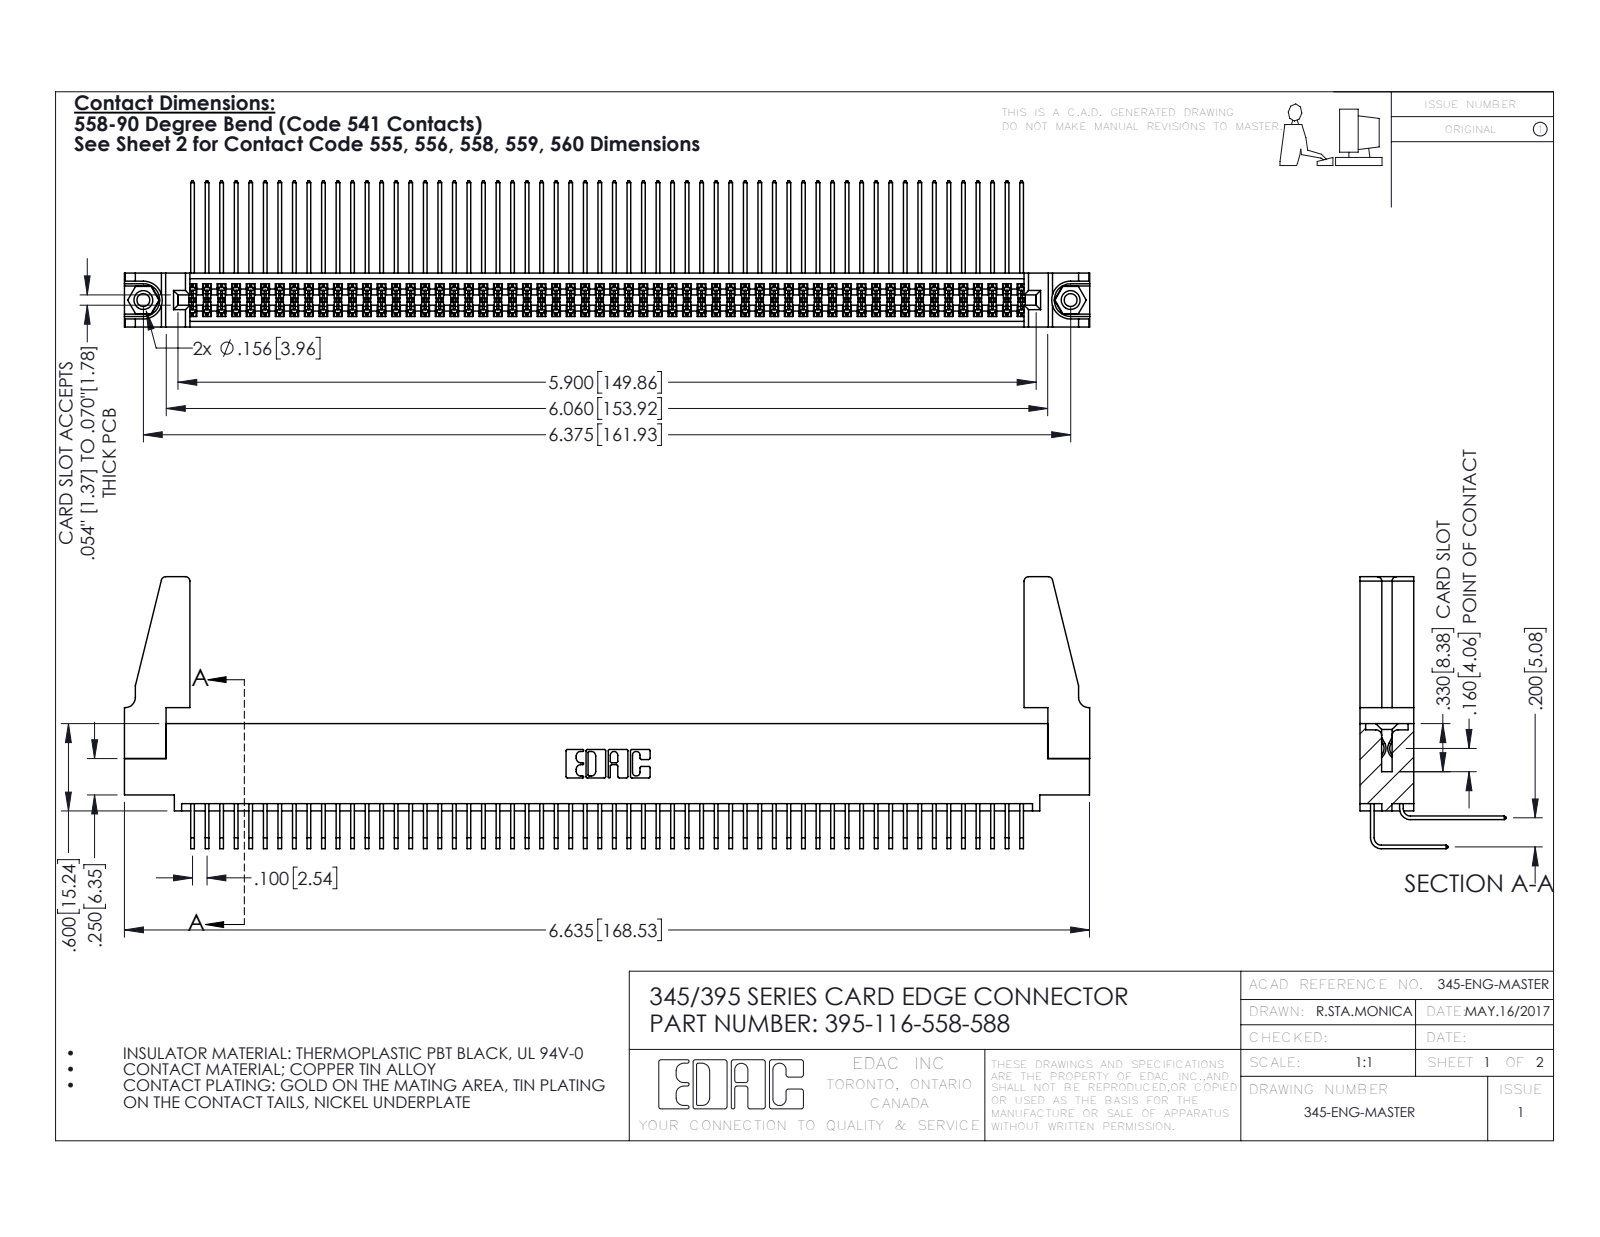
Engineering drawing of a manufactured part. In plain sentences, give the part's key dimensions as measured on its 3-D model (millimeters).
The part is named "395-116-558-588; 345-292-001_558 559 Tail - 1; 345-250-001_345-250-001-102; 345 Part_0.110 Offset - 0.156 Dia-TH (+2 more)". Its 3-D file was written by "SolidWorks 2016 (CONFIG_CONTROL_DESIGN)". It is 121 solids with 6286 faces: 4216 planar, 2054 cylindrical and 16 other. Overall it measures 168.6 by 47.5 by 25.5 millimeters. Its volume is 20 370 cubic millimeters and its surface area 31 970 square millimeters. Round holes: 2 of diameter 2.3, 2 of diameter 3.2, 2 of diameter 4, 1 of diameter 1.6. Round bosses or shafts: 2 of diameter 3.9. Partial cylindrical surfaces (rounded edges, fillets, slot ends): 174 of radius 0.2, 22 of radius 0.3, 8 of radius 0.8, 6 of radius 0.2, 6 of radius 0.8, 3 of radius 0.7, 2 of radius 0.4, 2 of radius 0.5. The main face-to-face distances are 1.8, 7.6, 5.1, 9.4, 2.5, 6.9, 0.6, 5.7, 0.6, 4.4. The hole center spacings are 6.9, 155.9, 161.9.
